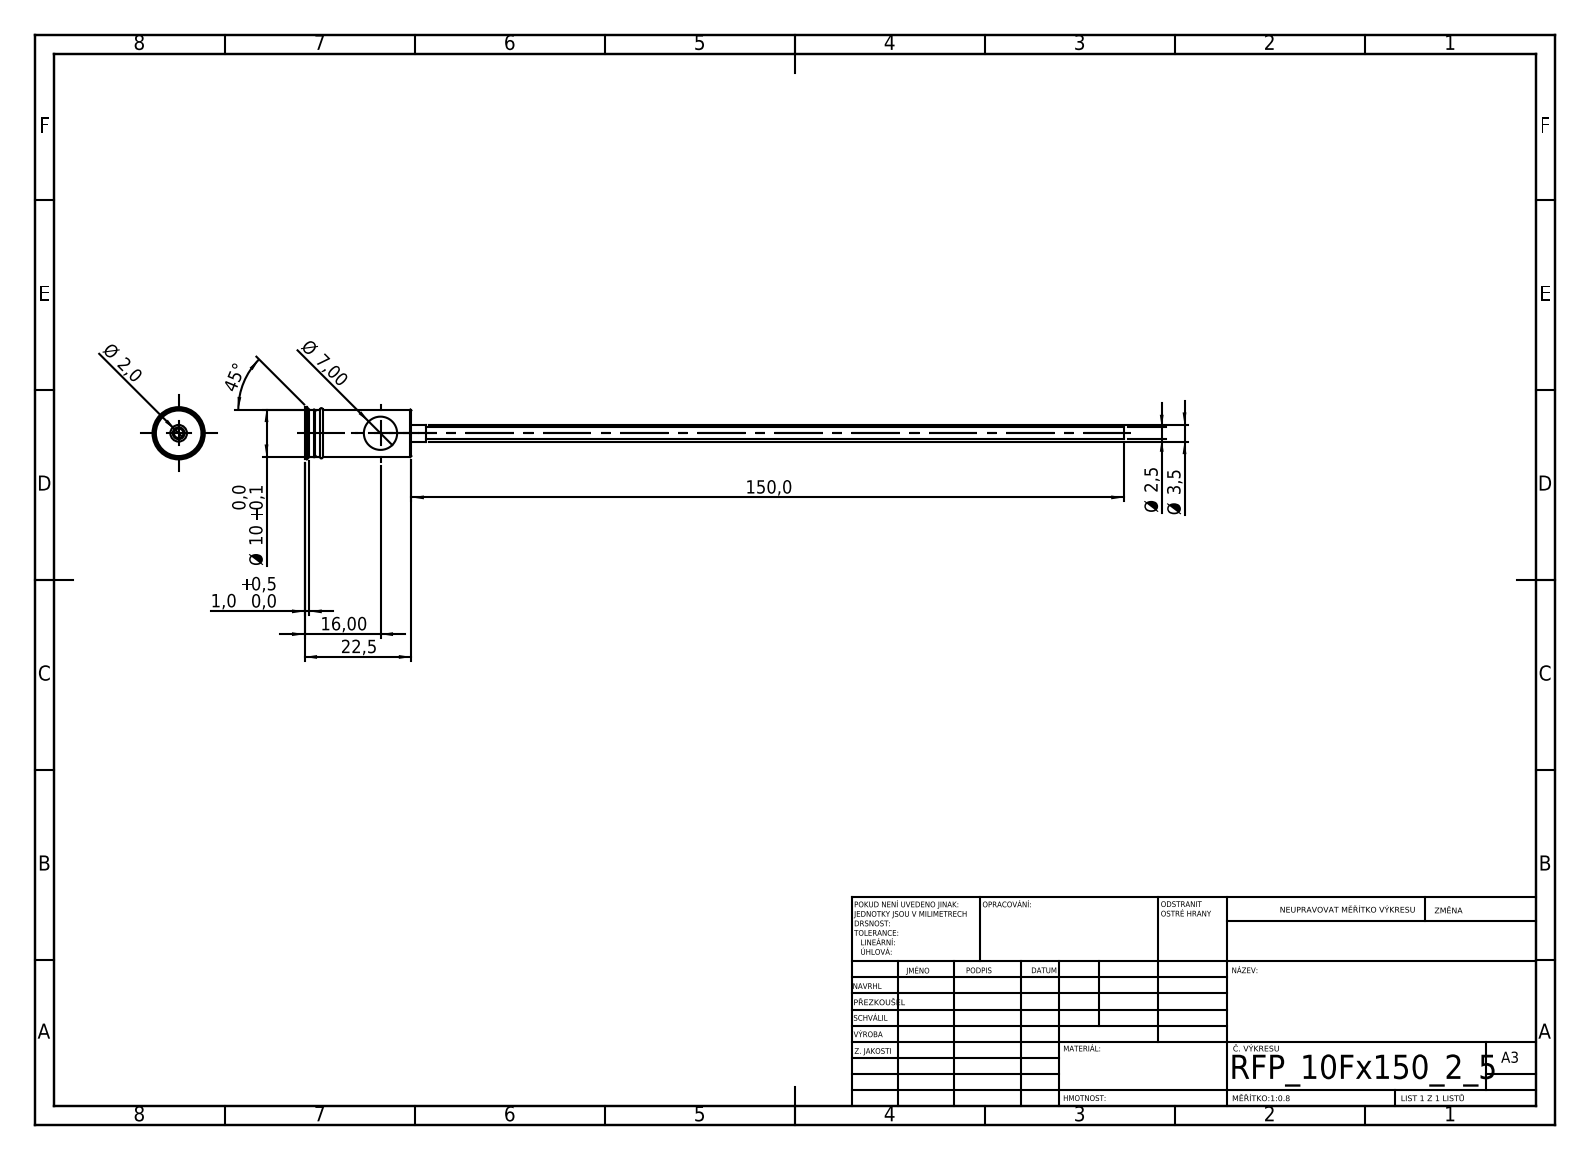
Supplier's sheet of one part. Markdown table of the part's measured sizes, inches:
| quantity | value |
| --- | --- |
| STEP written by | SolidWorks 2019 (CONFIG_CONTROL_DESIGN) |
| units | inches |
| bodies | 1 solid, 44 faces (20 planar, 16 cylindrical, 8 other) |
| overall size | 6.791 × 0.433 × 0.433 |
| volume | 0.1 in³ |
| surface area | 4.955 in² |
| round holes (diameter × count) | 0.079 × 1, 0.276 × 1 |
| round bosses / shafts (diameter × count) | 0.433 × 1, 0.394 × 1, 0.138 × 1, 0.098 × 1 |
| main face-to-face distances | 0.886, 0.807, 0.079, 0.213, 0.795, 0.091, 0.118, 0.913, 0.925, 1.004 |
